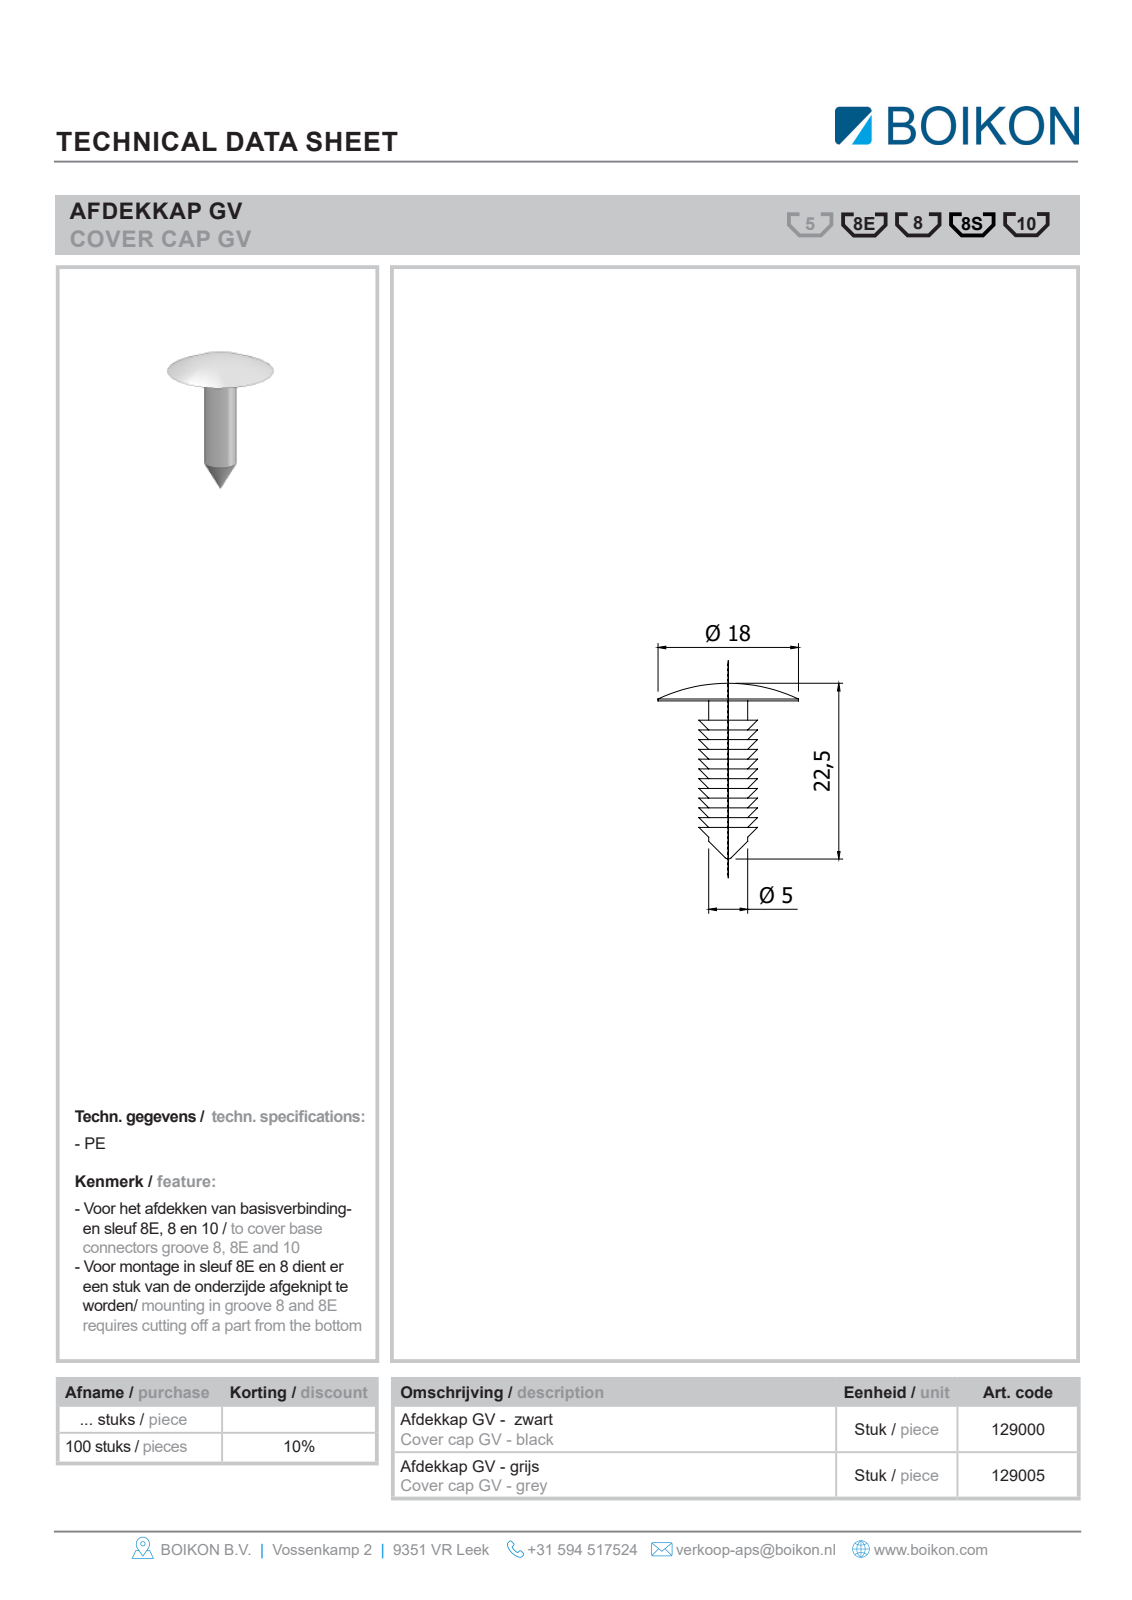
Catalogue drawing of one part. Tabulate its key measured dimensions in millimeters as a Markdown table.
| quantity | value |
| --- | --- |
| part name | Root; 129005Afdekkap voor inwendige verbinding GRIJSBOIKON |
| STEP written by | HiCAD 2013 1802.4 Build 509 (AUTOMOTIVE_DESIGN) |
| units | millimeters |
| bodies | 1 solid, 4 faces (1 planar, 1 cylindrical, 2 other) |
| overall size | 24 × 18 × 18 |
| volume | 762 mm³ |
| surface area | 842 mm² |
| round bosses / shafts (diameter × count) | 5.5 × 1 |
